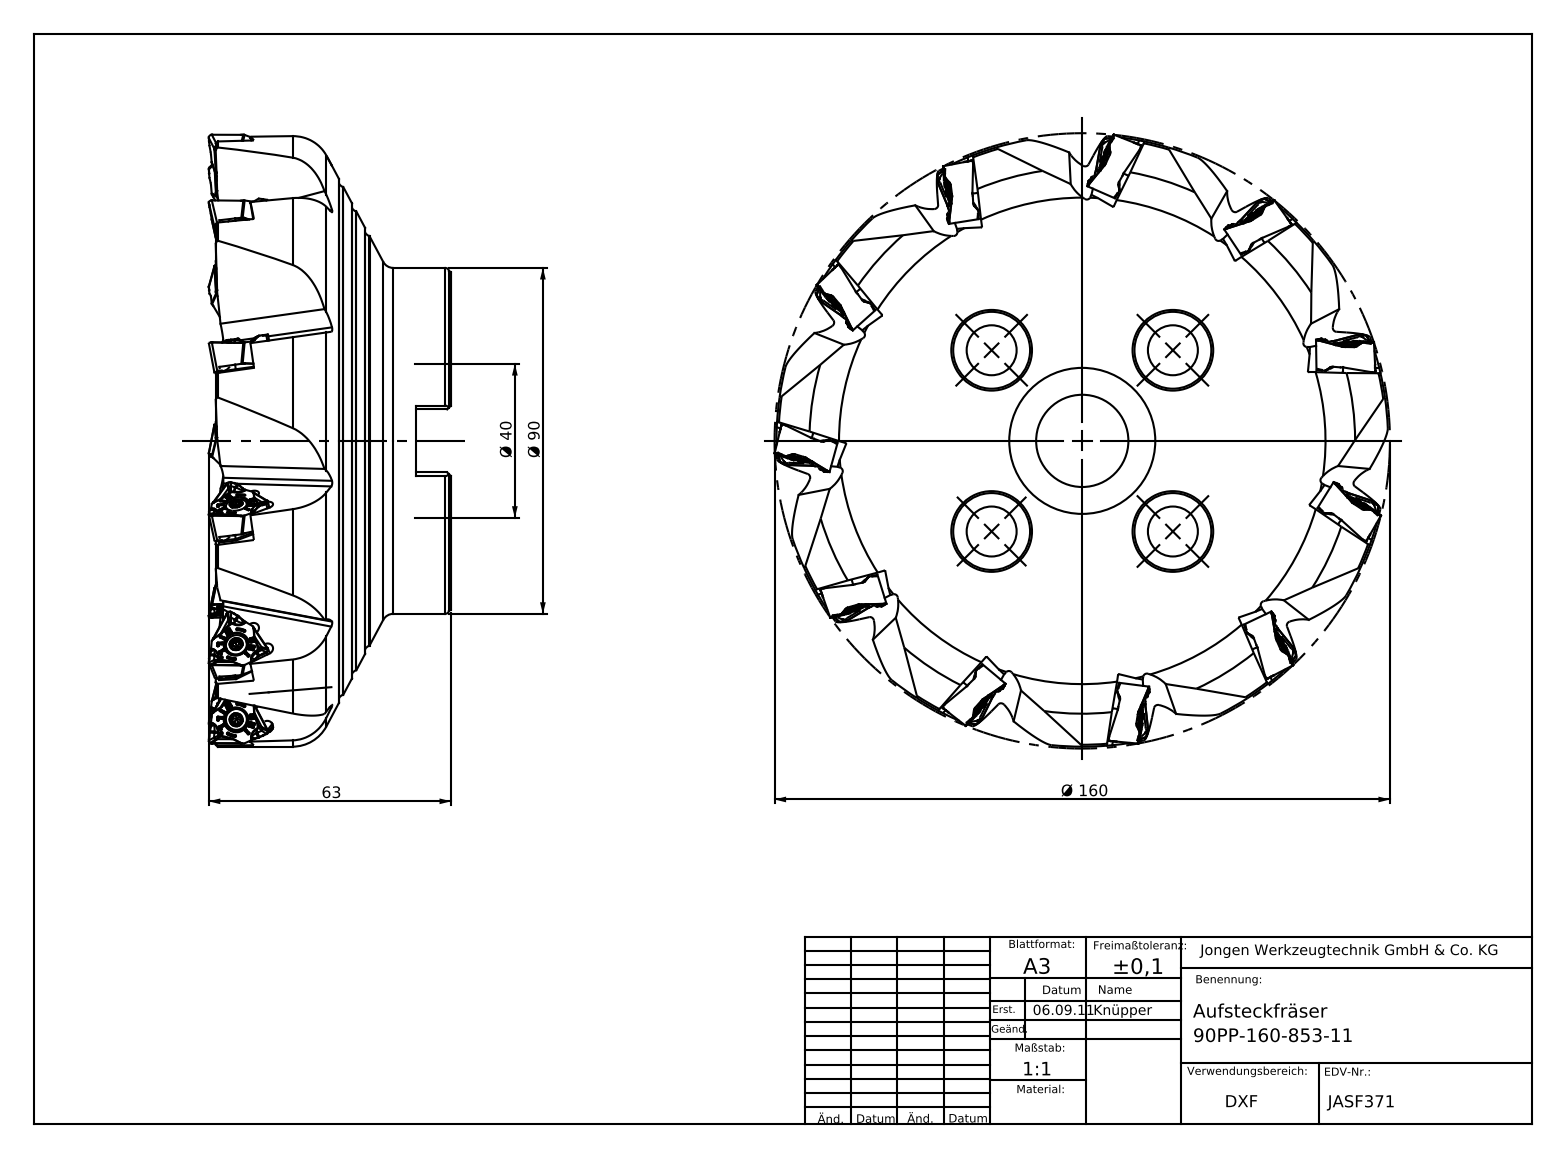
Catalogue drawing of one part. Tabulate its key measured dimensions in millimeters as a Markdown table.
| quantity | value |
| --- | --- |
| part name | 90PP-160-853-11 |
| STEP written by | SolidWorks 2010 (AUTOMOTIVE_DESIGN) |
| units | millimeters |
| bodies | 1 solid, 601 faces (170 planar, 197 cylindrical, 234 other) |
| overall size | 160 × 160 × 63 |
| volume | 688 403 mm³ |
| surface area | 86 425 mm² |
| round holes (diameter × count) | 13 × 4, 20 × 4, 24 × 1, 40 × 1, 40.15 × 1, 40.3 × 1 |
| round bosses / shafts (diameter × count) | 160 × 1, 159.15 × 1, 90 × 1 |
| partial cylindrical surfaces (radius × count) | 0.3 × 77, 1.5 × 22, 1.65 × 11 |
| main face-to-face distances | 59.25, 61.2, 1.95, 9, 50.25, 52.2, 31, 22, 28.25, 30.2 |
| hole center spacings | 33.35, 47.16, 66.69 |
